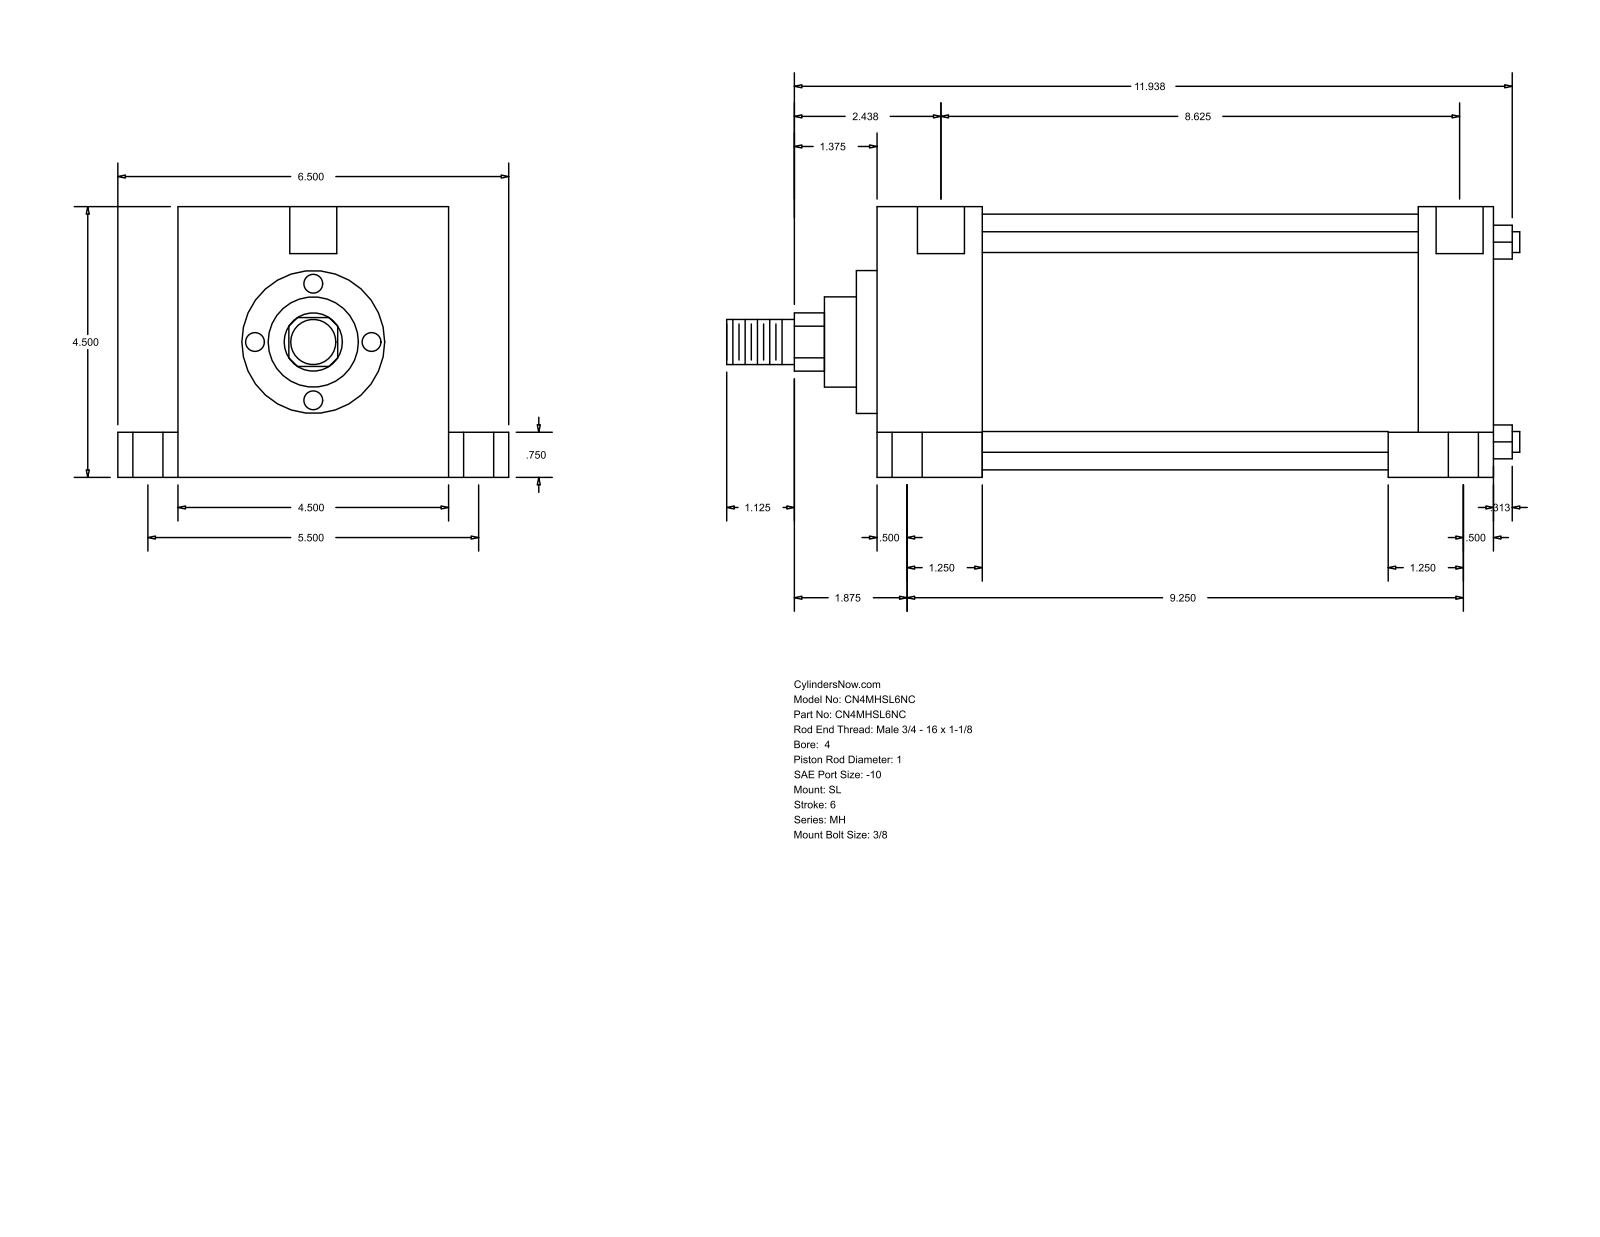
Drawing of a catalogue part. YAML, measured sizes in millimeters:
part_name: "MH_SL__0400_1"
step_written_by: "GSSL Pune (CONFIG_CONTROL_DESIGN)"
units: millimeters
bodies: {solids: 0, faces: 110, planar: 77, cylindrical: 33, other: 0}
overall_size: [334.96, 165.1, 114.3]
round_holes:
  - {diameter: 8.73, count: 4}
  - {diameter: 12.7, count: 4}
  - {diameter: 19.05, count: 4}
  - {diameter: 19.84, count: 2}
round_bosses_or_shafts:
  - {diameter: 8.76, count: 4}
  - {diameter: 107.95, count: 1}
  - {diameter: 60.33, count: 1}
  - {diameter: 38.1, count: 1}
  - {diameter: 25.4, count: 1}
  - {diameter: 19.05, count: 1}
partial_cylinders:
  - {radius: 12.29, count: 1}
face_to_face_distances: [114.3, 260.35, 44.46, 215.89, 228.6, 184.14, 31.75, 25.4, 139.7, 19.05]
hole_center_spacings: [1.58, 69.85, 69.87, 71, 71.3, 139.7, 220.66, 222.24]
